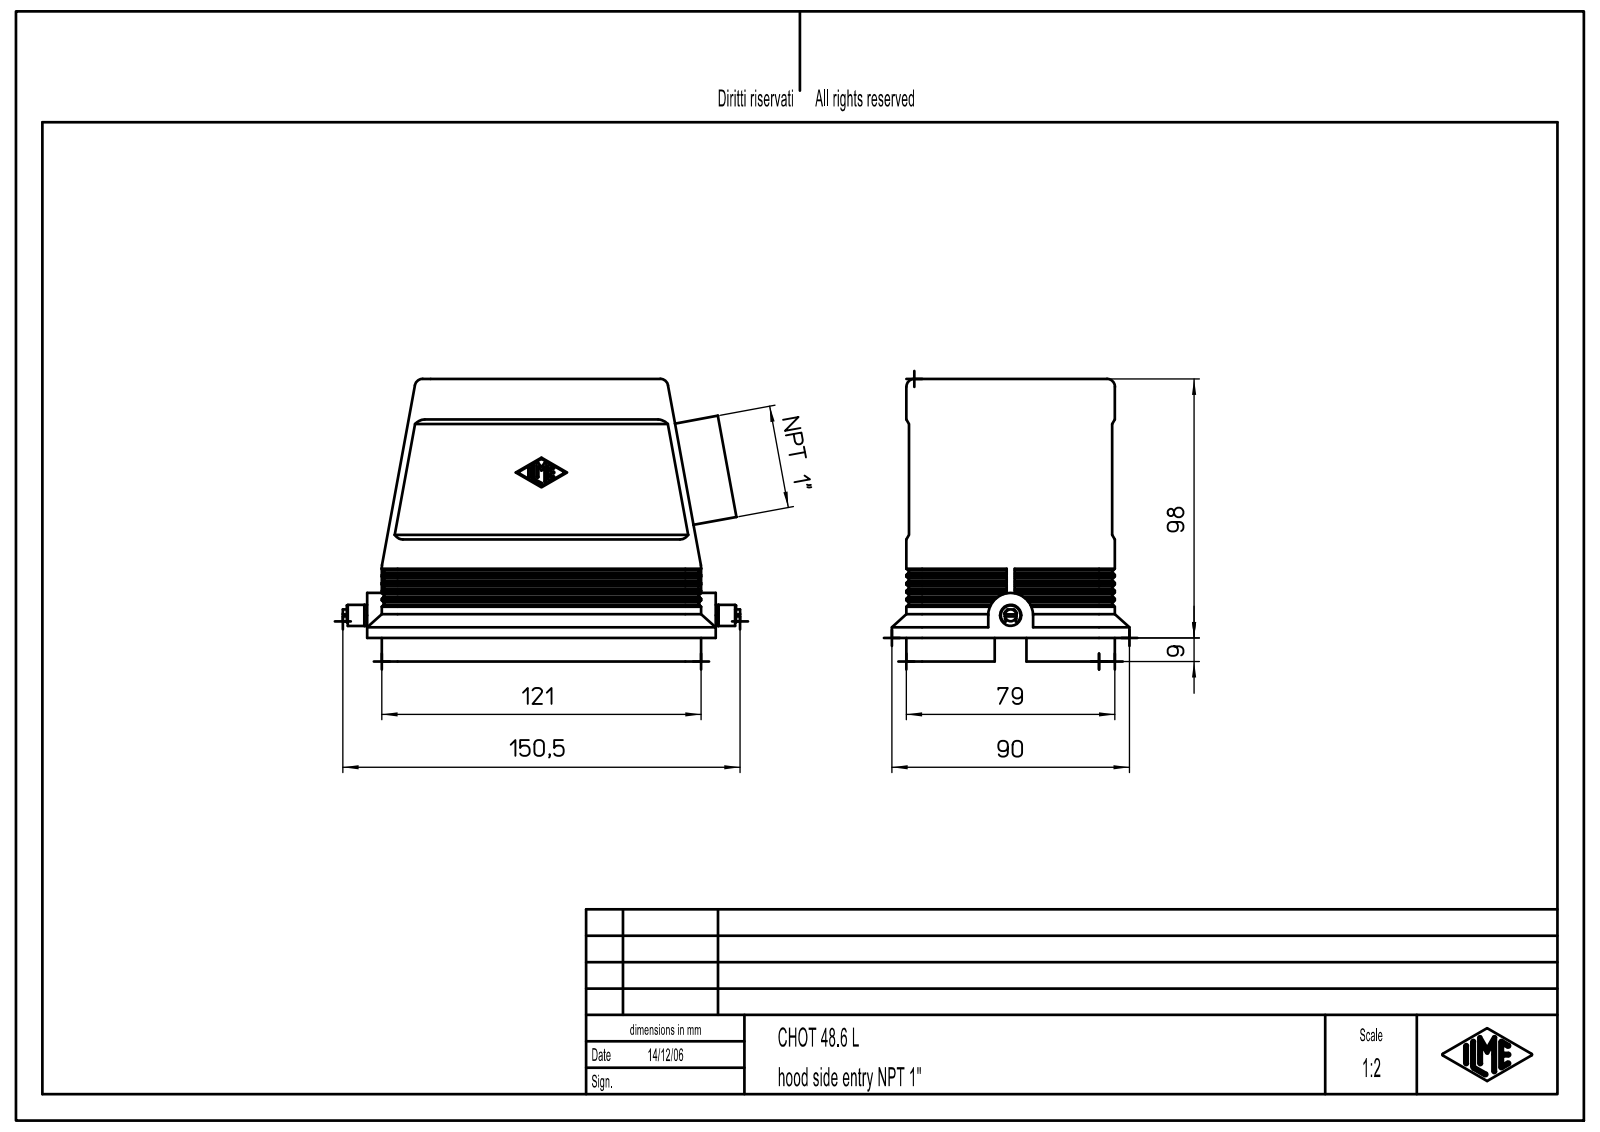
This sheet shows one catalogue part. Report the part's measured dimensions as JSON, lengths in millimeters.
{"part_name": "MSBO11589", "step_written_by": "Creo Elements/Direct Modeling 18.0B 02-Dec-2011 (C) Parametric Technology GmbH (AUTOMOTIVE_DESIGN)", "units": "millimeters", "bodies": {"solids": 1, "faces": 587, "planar": 313, "cylindrical": 188, "other": 86}, "overall_size": [150.5, 107, 90], "volume_mm3": 249685, "surface_area_mm2": 101345, "round_holes": [[3.5, 8], [2.46, 5], [2.46, 3], [6, 1], [48, 1]], "round_bosses_or_shafts": [[46, 1], [43, 1], [40, 1], [8, 1], [4.5, 1], [3.5, 1]], "partial_cylinders_radius": [[0.38, 14], [2, 12], [6, 10], [0.5, 4], [3, 4], [5, 4], [11.5, 4], [0.95, 3]], "face_to_face_distances": [2.5, 74.5, 72, 3.5, 1, 75.5, 78, 13, 77, 8.5], "hole_center_spacings": [27, 35, 104, 107.45, 109.73, 8, 62, 104.31]}
